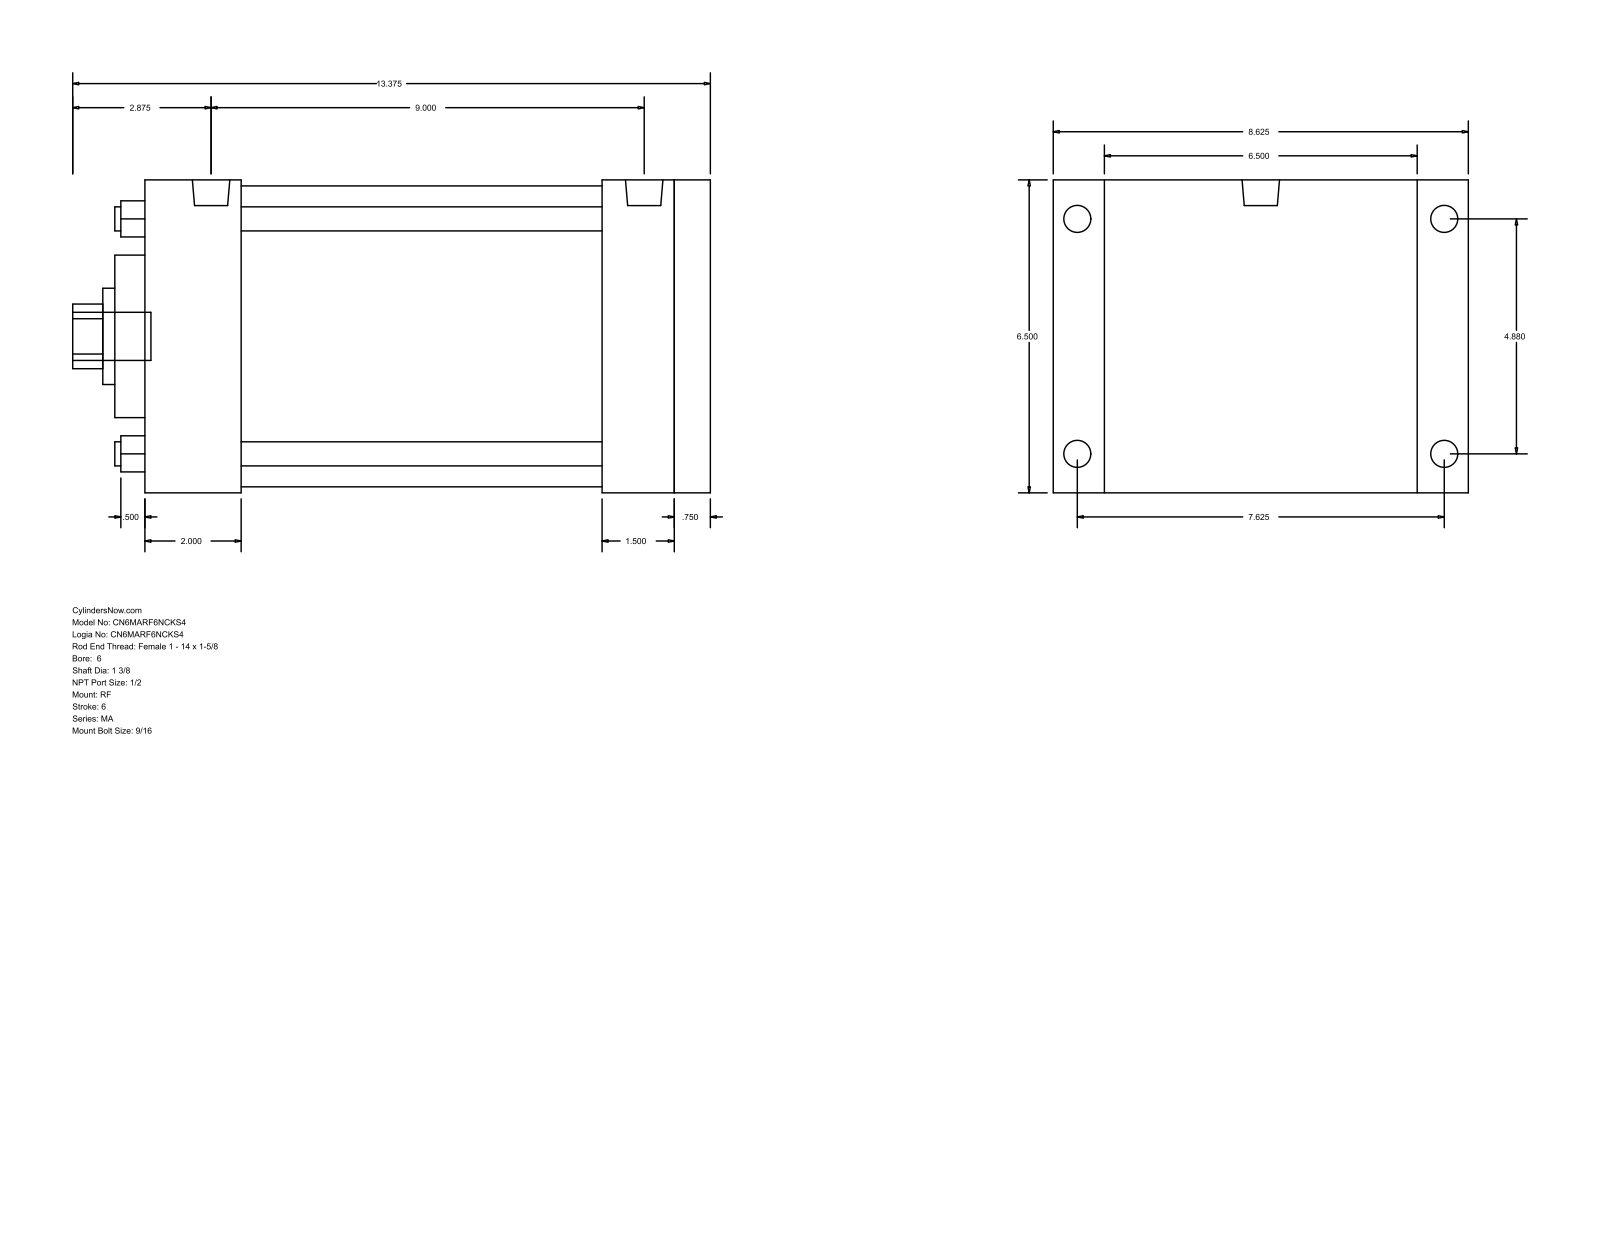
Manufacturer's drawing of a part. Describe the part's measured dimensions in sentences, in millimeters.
The part is named "MA_RF__0600_1.375". Its 3-D file was written by "GSSL Pune (CONFIG_CONTROL_DESIGN)". It is 0 solids with 94 faces: 65 planar, 29 cylindrical and 0 other. Overall it measures 339.73 by 219.07 by 165.1 millimeters. Round holes: 4 of diameter 12.7, 1 of diameter 34.92, 1 of diameter 50.8, 1 of diameter 85.72, 1 of diameter 158.75. Round bosses or shafts: 4 of diameter 17.46, 4 of diameter 14.29, 2 of diameter 19.77, 1 of diameter 25.4. Partial cylindrical surfaces (rounded edges, fillets, slot ends): 1 of radius 17.06. The main face-to-face distances are 165.1, 301.63, 19.05, 282.58, 50.8, 231.78, 250.83, 244.47, 193.67, 38.11. The hole center spacings are 87.65, 123.96, 175.31.
